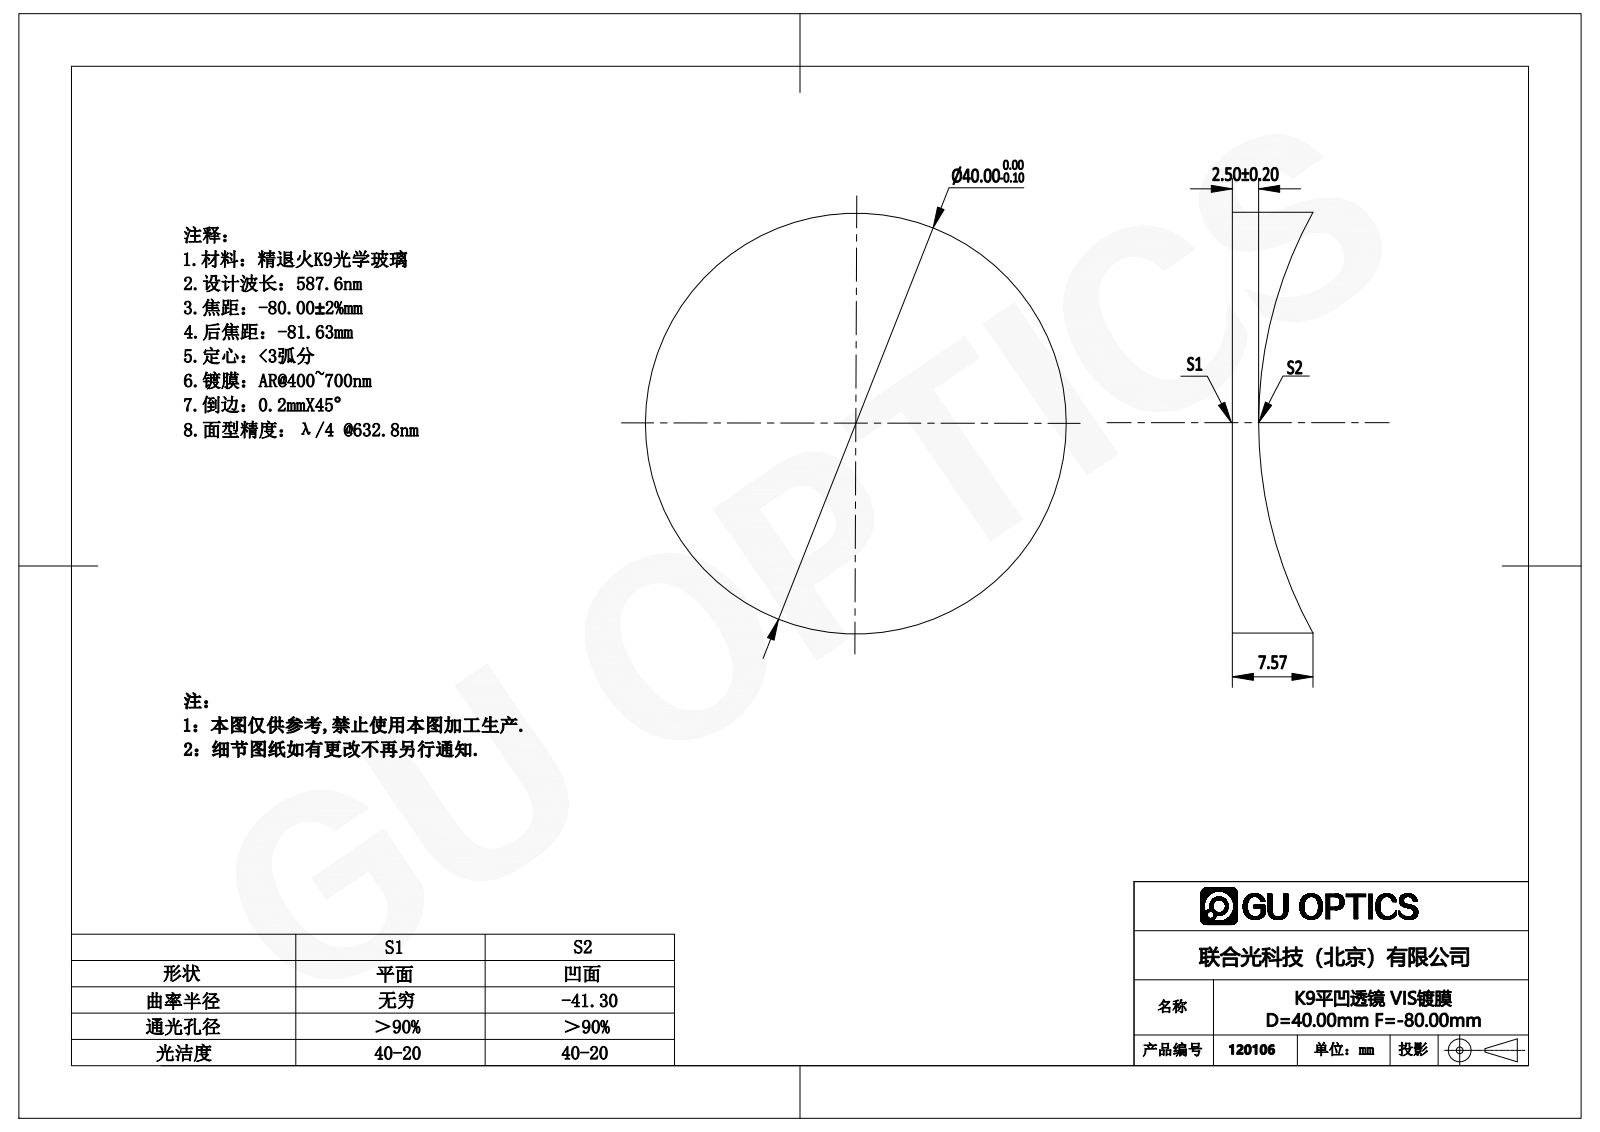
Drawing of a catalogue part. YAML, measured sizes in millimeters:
part_name: "120046"
step_written_by: "SolidWorks 2016 (AUTOMOTIVE_DESIGN)"
units: millimeters
bodies: {solids: 1, faces: 5, planar: 1, cylindrical: 2, other: 2}
overall_size: [40, 40, 7.67]
volume: 6315
surface_area: 3560
round_bosses_or_shafts:
  - {diameter: 40, count: 1}
